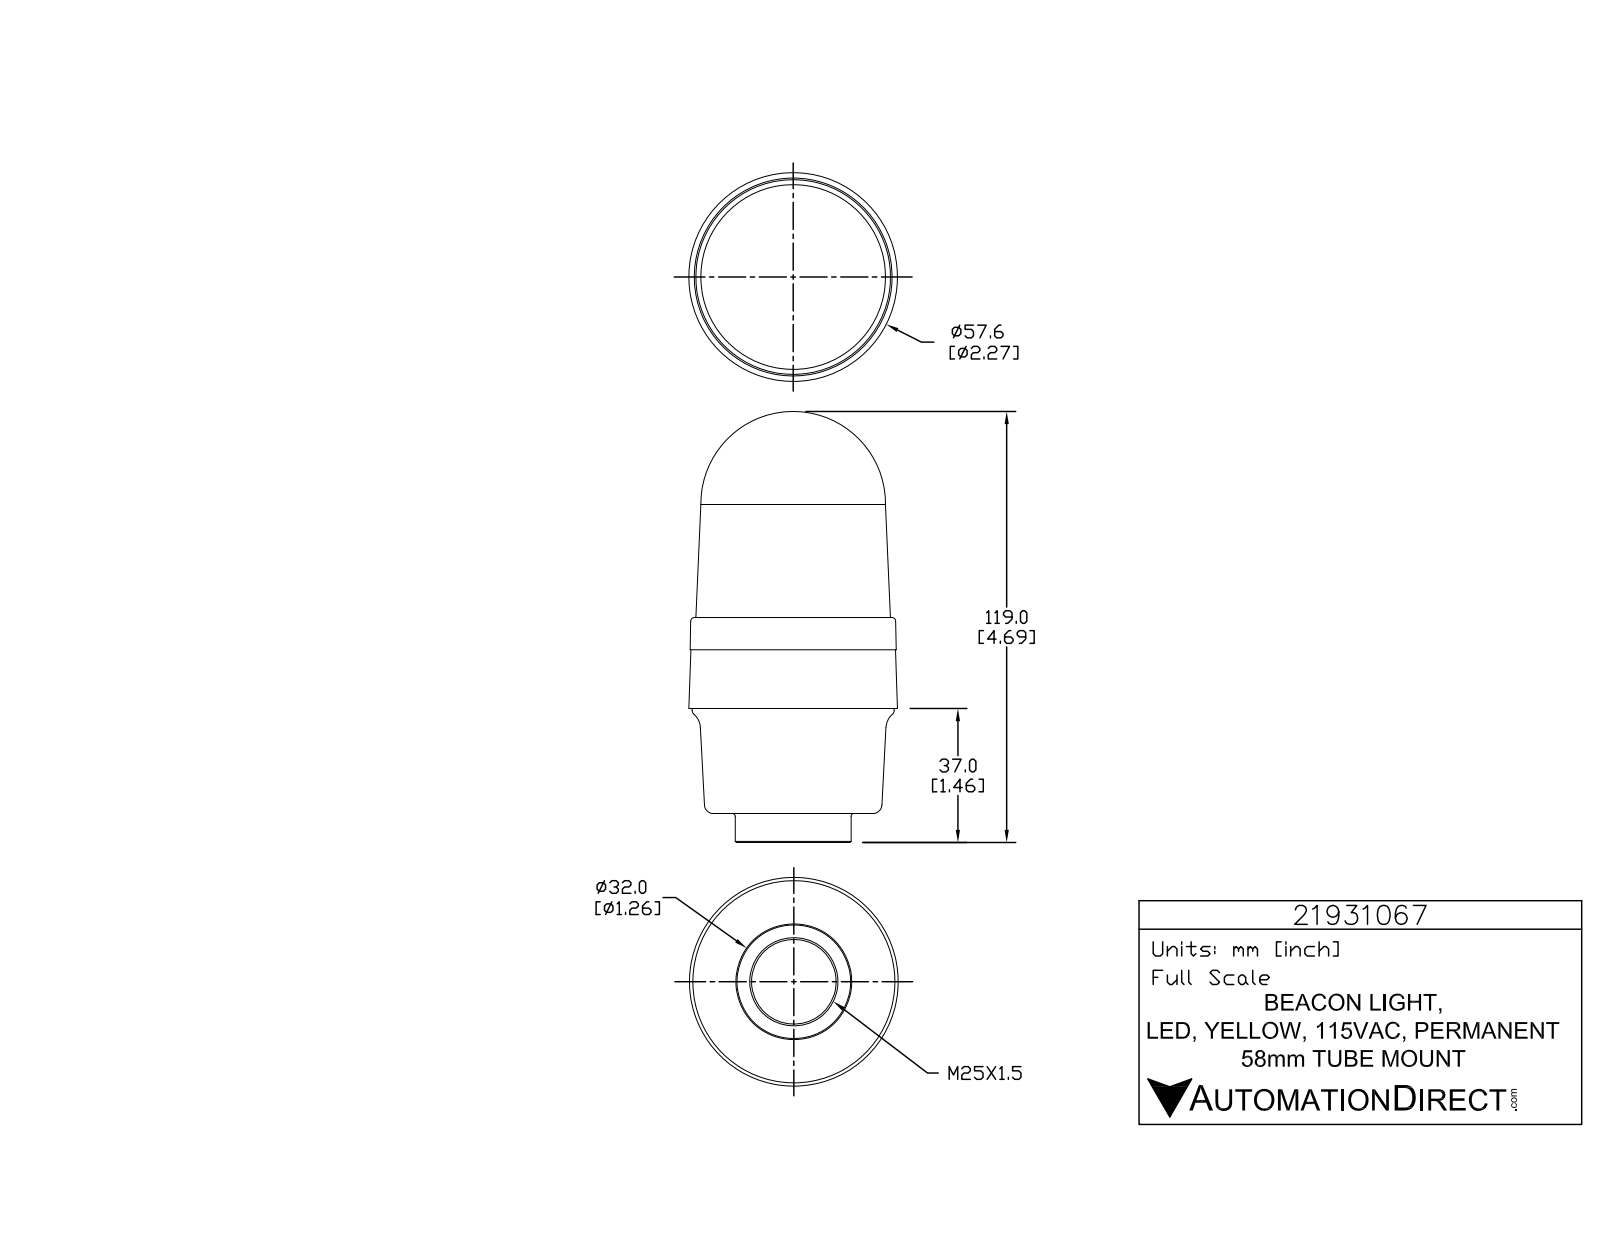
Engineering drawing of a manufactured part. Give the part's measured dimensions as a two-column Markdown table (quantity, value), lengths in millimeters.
| quantity | value |
| --- | --- |
| part name | 21931067 |
| STEP written by | SolidWorks 2015 (AUTOMOTIVE_DESIGN) |
| units | millimeters |
| bodies | 1 solid, 791 faces (525 planar, 168 cylindrical, 98 other) |
| overall size | 119 × 57.6 × 57.6 |
| volume | 227 600 mm³ |
| surface area | 21 970 mm² |
| round holes (diameter × count) | 1 × 3, 23.4 × 1 |
| round bosses / shafts (diameter × count) | 5.7 × 3, 1.4 × 3, 55.8 × 1, 32 × 1 |
| partial cylindrical surfaces (radius × count) | 0.2 × 6, 0.2 × 6, 0.2 × 6, 3.3 × 6, 0.1 × 3, 0.1 × 3, 0.2 × 3, 0.2 × 3 |
| main face-to-face distances | 8, 29, 37, 25.1, 54.1, 62.1, 8.9, 16.2, 45.2, 53.2 |
